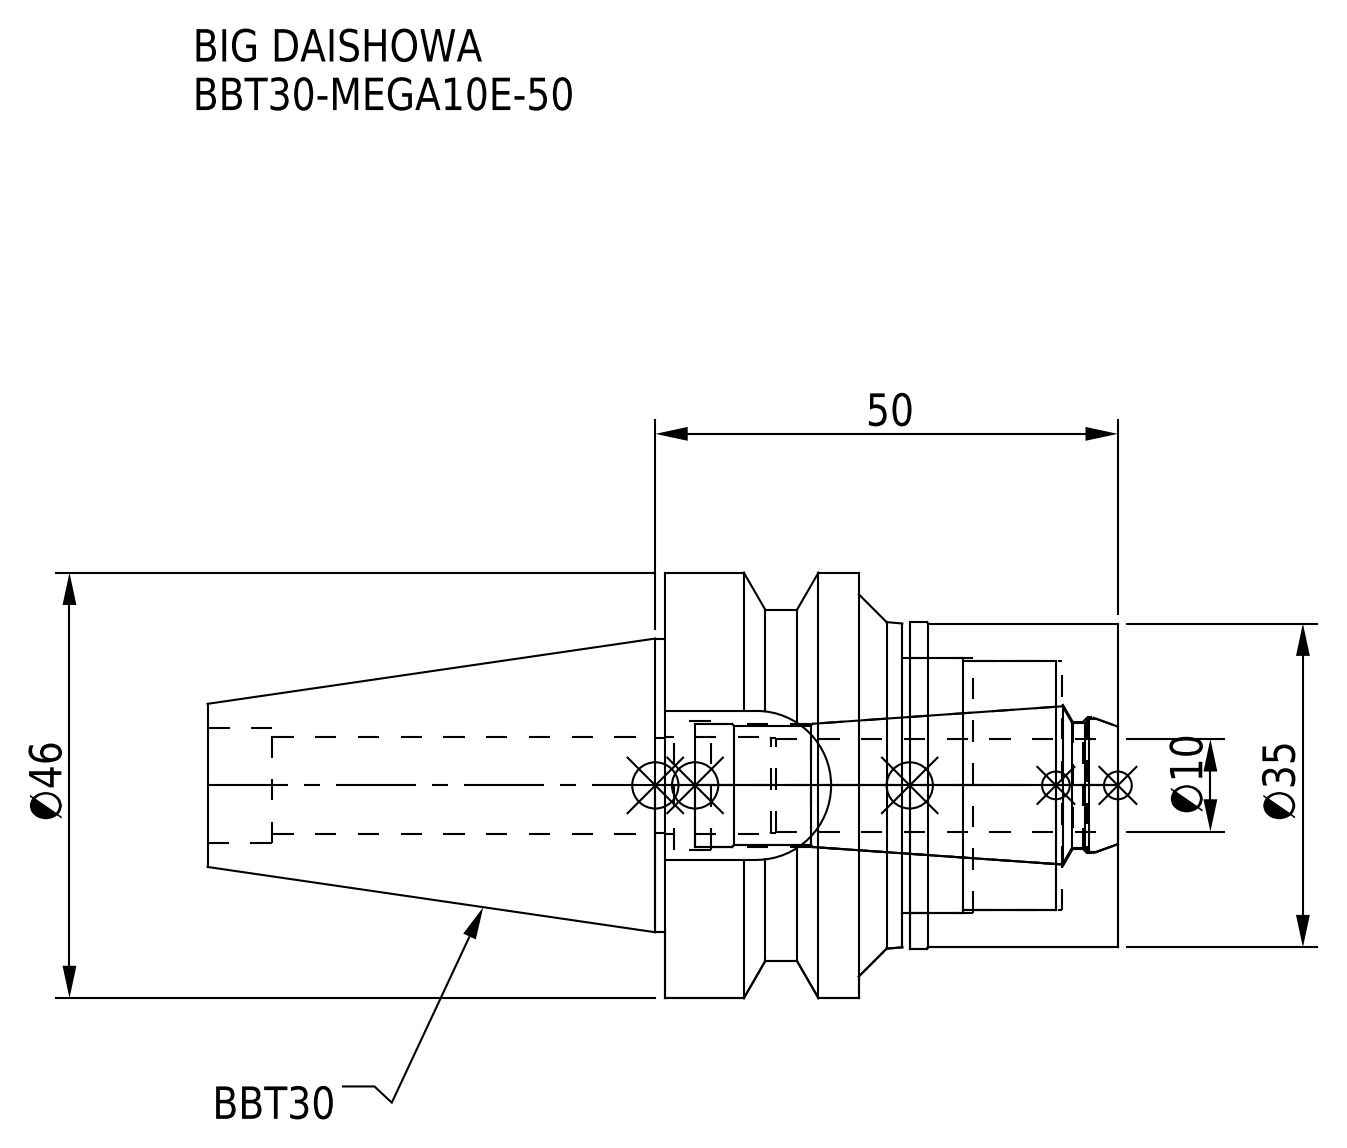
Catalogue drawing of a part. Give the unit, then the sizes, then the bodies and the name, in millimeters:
Units: millimetres
Overall size (bounding box): 98.4 × 46 × 46
Round holes (diameter × count): ⌀10.2 ×1, ⌀10.4 ×1, ⌀12.5 ×1, ⌀13.3 ×1, ⌀13.8 ×1, ⌀13.9 ×1, ⌀14.7 ×1, ⌀27 ×1, ⌀27.5 ×1
Round bosses / shafts (diameter × count): ⌀46 ×1, ⌀35.3 ×1, ⌀35 ×1, ⌀31.75 ×1
Partial cylindrical surfaces — rounded edges, fillets, slot ends (radius × count): R8.05 ×1, R19 ×1
Main face-to-face distances: 49, 22.5, 26.5, 23.3, 0.8, 25.7, 6.7, 15.8, 16.6, 42.3
Volume: 68 268 mm³ · Surface area: 21 128 mm²
Bodies: 2 solids, 79 faces (21 planar, 38 cylindrical, 20 other)
Part name (STEP PRODUCT): MEN10_1.stp; BBT30-MEGA10E-50-100-FreeParts; BBT30-MEGA10E-50_1.stp; BBT30-MEGA10E-50-100.stp (+3 more)
STEP written by: SolidWorks 2019 (CONFIG_CONTROL_DESIGN)
